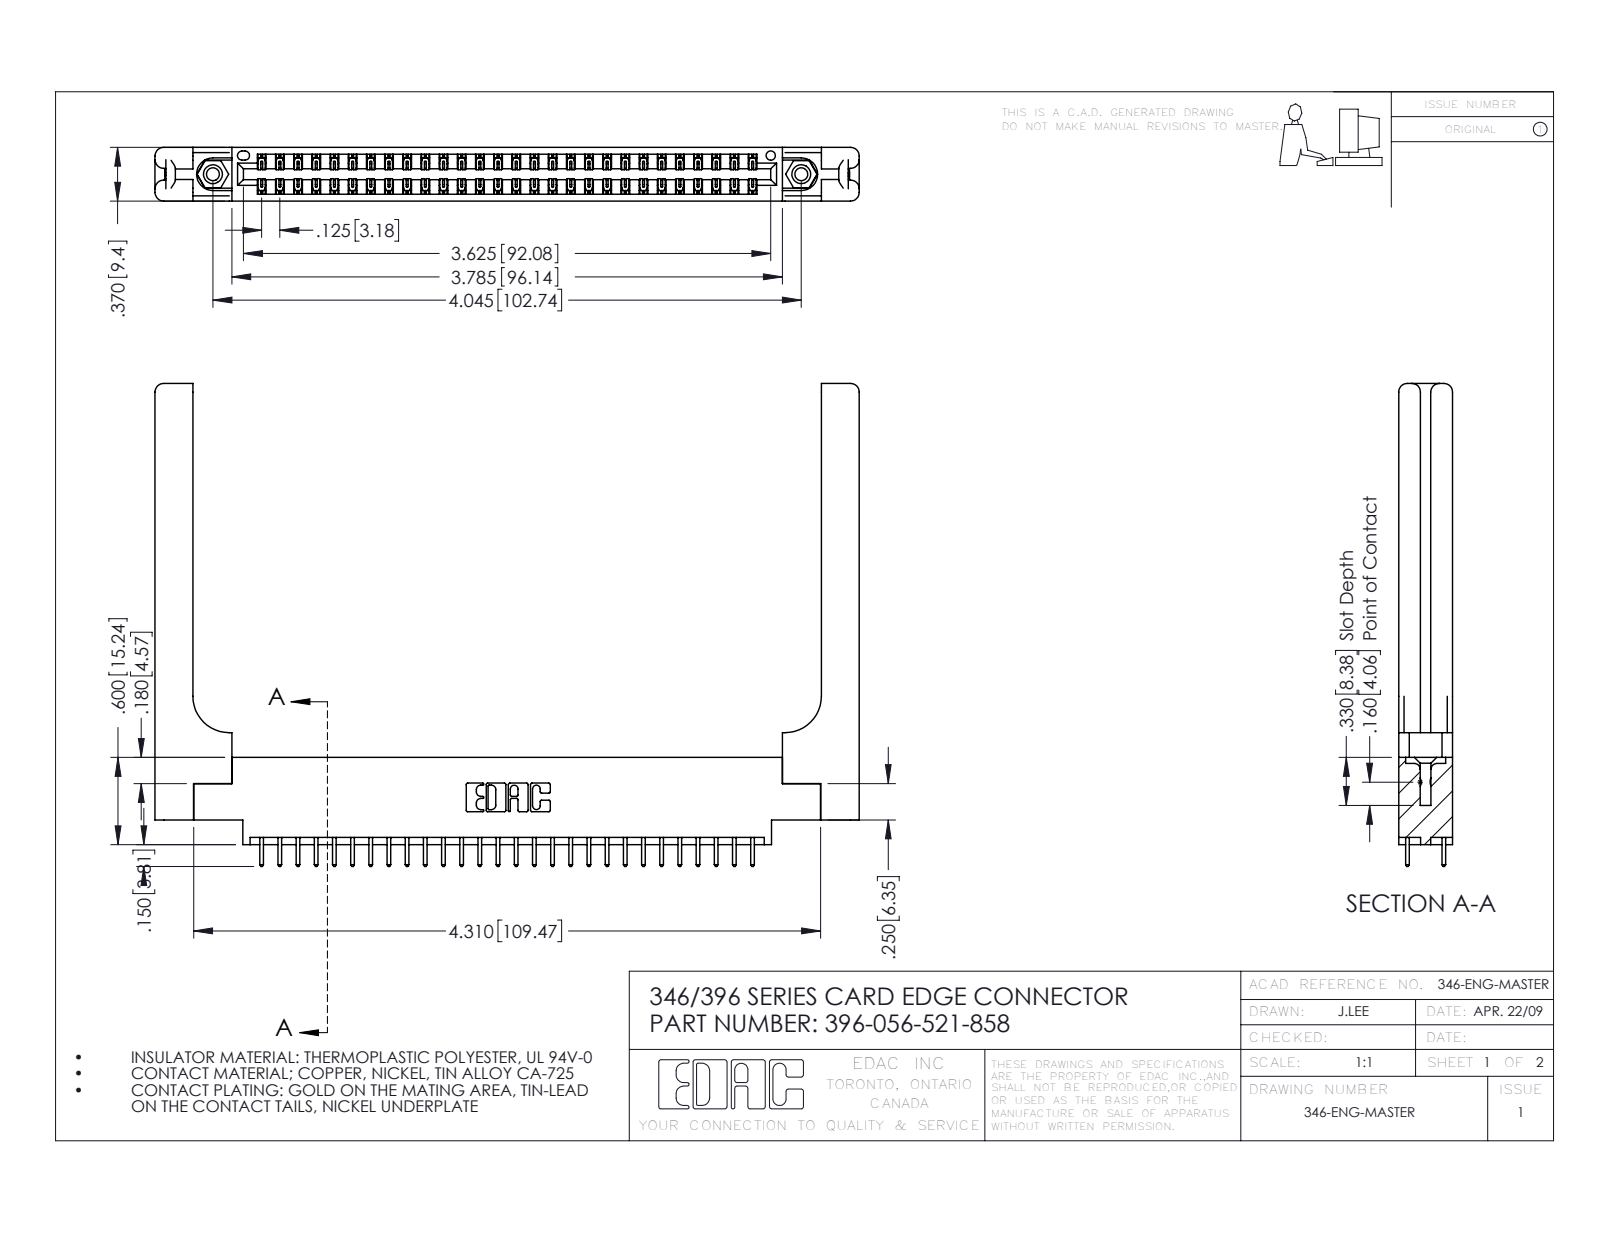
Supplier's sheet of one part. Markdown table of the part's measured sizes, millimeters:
| quantity | value |
| --- | --- |
| part name | 396-056-521-858; 346-220-058_345-220-058; 345-292-001_345-293-121; 346 Part_0.170 Offset - 0.156 Dia-TH (+1 more) |
| STEP written by | SolidWorks 2016 (CONFIG_CONTROL_DESIGN) |
| units | millimeters |
| bodies | 61 solids, 3294 faces (2188 planar, 1046 cylindrical, 60 other) |
| overall size | 123 × 84.3 × 9.4 |
| volume | 19 210 mm³ |
| surface area | 20 860 mm² |
| round holes (diameter × count) | 2.3 × 2, 3.2 × 2, 4 × 2, 1.6 × 1 |
| round bosses / shafts (diameter × count) | 3.9 × 2 |
| partial cylindrical surfaces (radius × count) | 0.2 × 84, 0.3 × 56, 0.3 × 22, 1.5 × 16, 0.2 × 6, 0.8 × 6, 0.7 × 3, 0.4 × 2 |
| main face-to-face distances | 9.4, 1.2, 8.2, 1.8, 3.8, 3.8, 6.4, 0.6, 7.6, 7 |
| hole center spacings | 6.2, 97.5, 102.7 |
